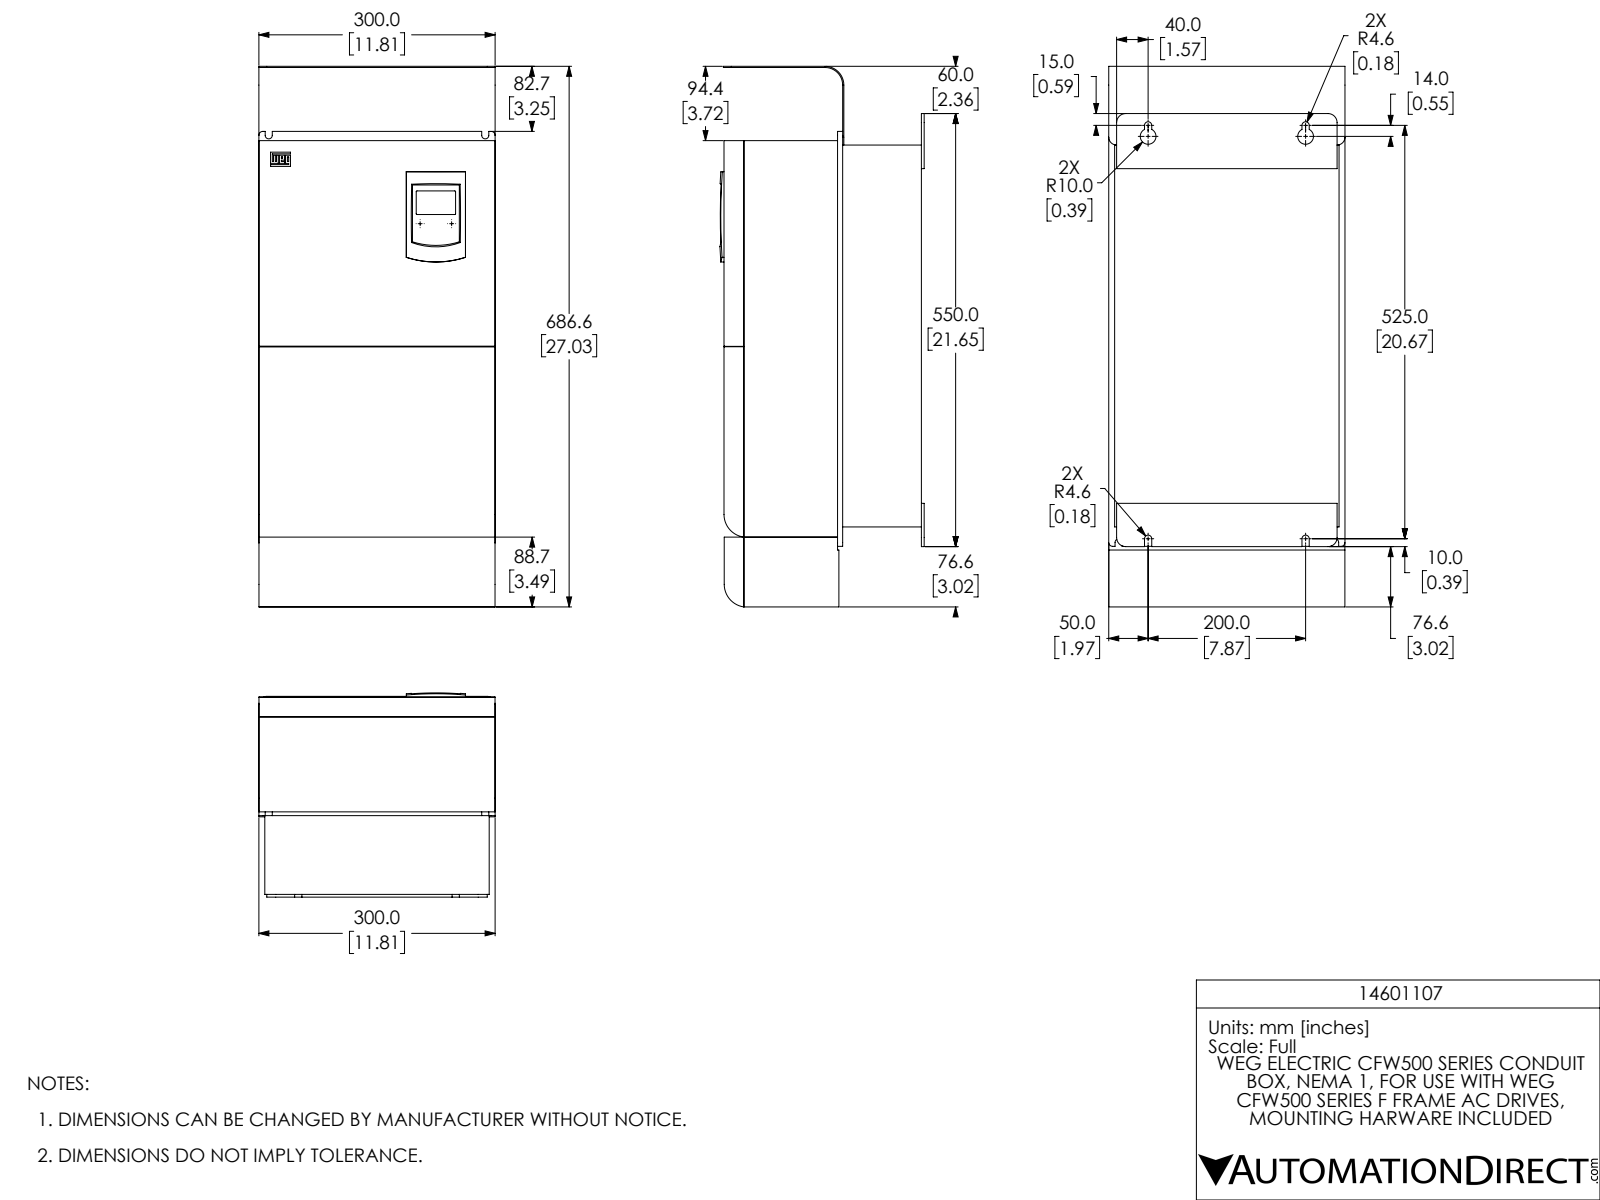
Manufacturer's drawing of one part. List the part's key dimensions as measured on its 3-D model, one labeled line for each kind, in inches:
Part name (STEP PRODUCT): CFW500F Nema I nc
STEP written by: SolidWorks 2017 (AUTOMOTIVE_DESIGN)
Units: inches
Bodies: 5 solids, 180 faces (143 planar, 34 cylindrical, 3 other)
Overall size (bounding box): 27.031 × 11.811 × 10.213
Volume: 2 479 in³ · Surface area: 2 191 in²
Round holes (diameter × count): ⌀0.787 ×2
Partial cylindrical surfaces — rounded edges, fillets, slot ends (radius × count): R0.039 ×4, R0.177 ×4, R0.181 ×4, R0.197 ×4, R0.394 ×4, R0.453 ×4, R1.142 ×2, R0.88 ×1
Main face-to-face distances: 8.874, 9.87, 0.996, 0.291, 11.512, 11.803, 3.937, 0.059, 3.878, 11.22
Hole centre spacings: 7.874
